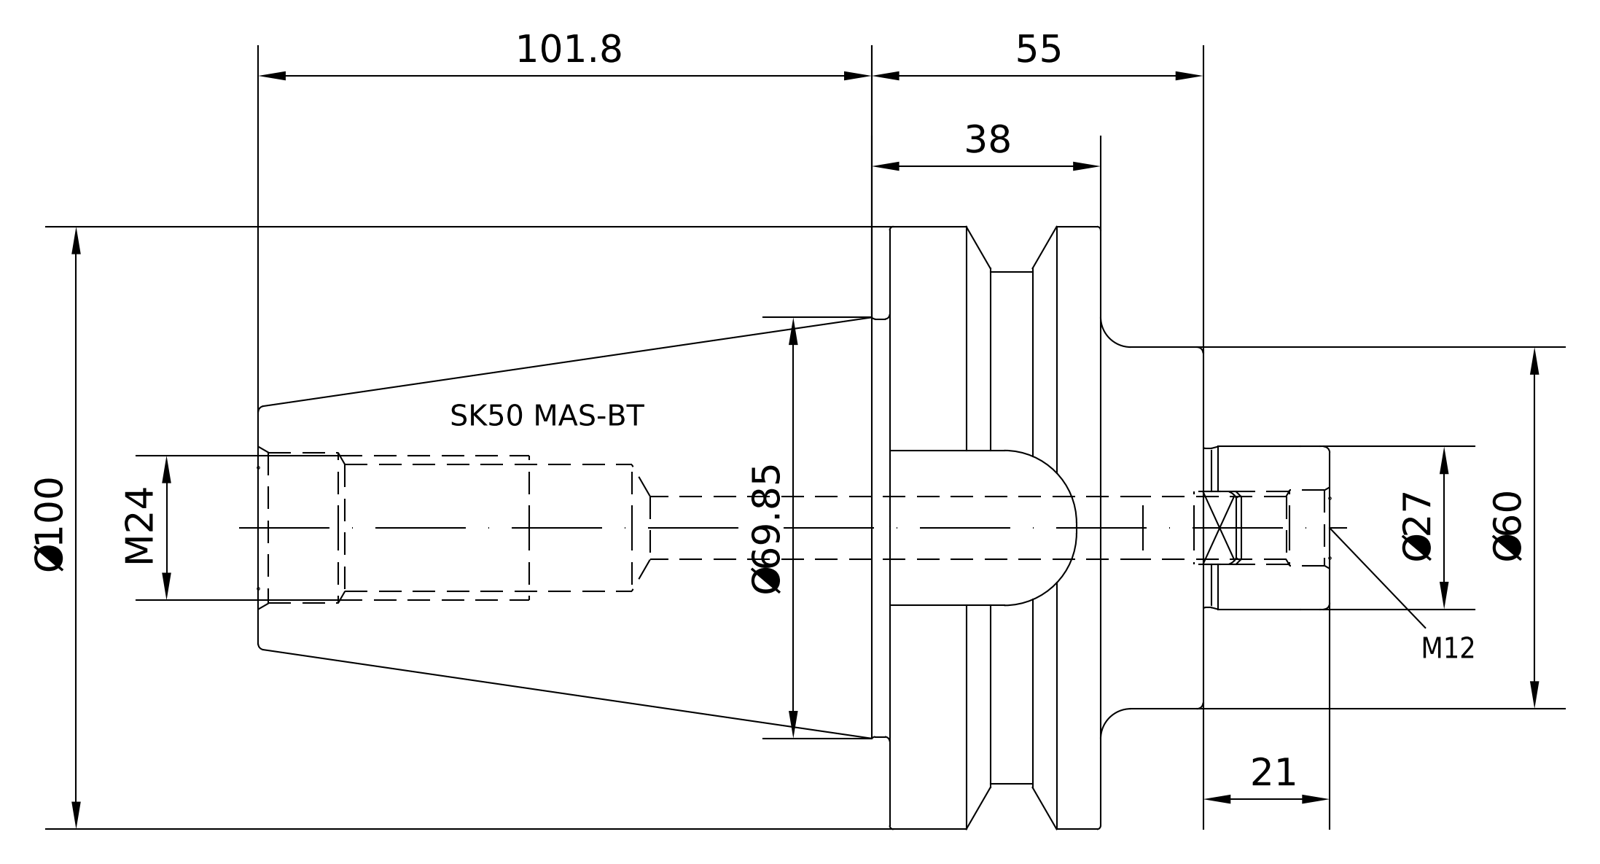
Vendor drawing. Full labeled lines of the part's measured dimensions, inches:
Part name (STEP PRODUCT): 50-550-27
STEP written by: PRO/ENGINEER BY PARAMETRIC TECHNOLOGY CORPORATION, 2010430 (CONFIG_CONTROL_DESIGN)
Units: inches
Bodies: 1 solid, 113 faces (37 planar, 26 cylindrical, 50 other)
Overall size (bounding box): 7 × 3.936 × 3.936
Volume: 32.23 in³ · Surface area: 91.51 in²
Round holes (diameter × count): ⌀0.402 ×1, ⌀0.472 ×1, ⌀0.817 ×1, ⌀0.985 ×1, ⌀1.012 ×1
Round bosses / shafts (diameter × count): ⌀3.936 ×1, ⌀3.337 ×1, ⌀2.722 ×1, ⌀2.362 ×1, ⌀1.063 ×1, ⌀0.945 ×1
Partial cylindrical surfaces — rounded edges, fillets, slot ends (radius × count): R0.508 ×1
Main face-to-face distances: 1.378, 2.047, 0.669, 2.772, 4.126, 5.504, 6.173, 7, 2.874, 1.496
